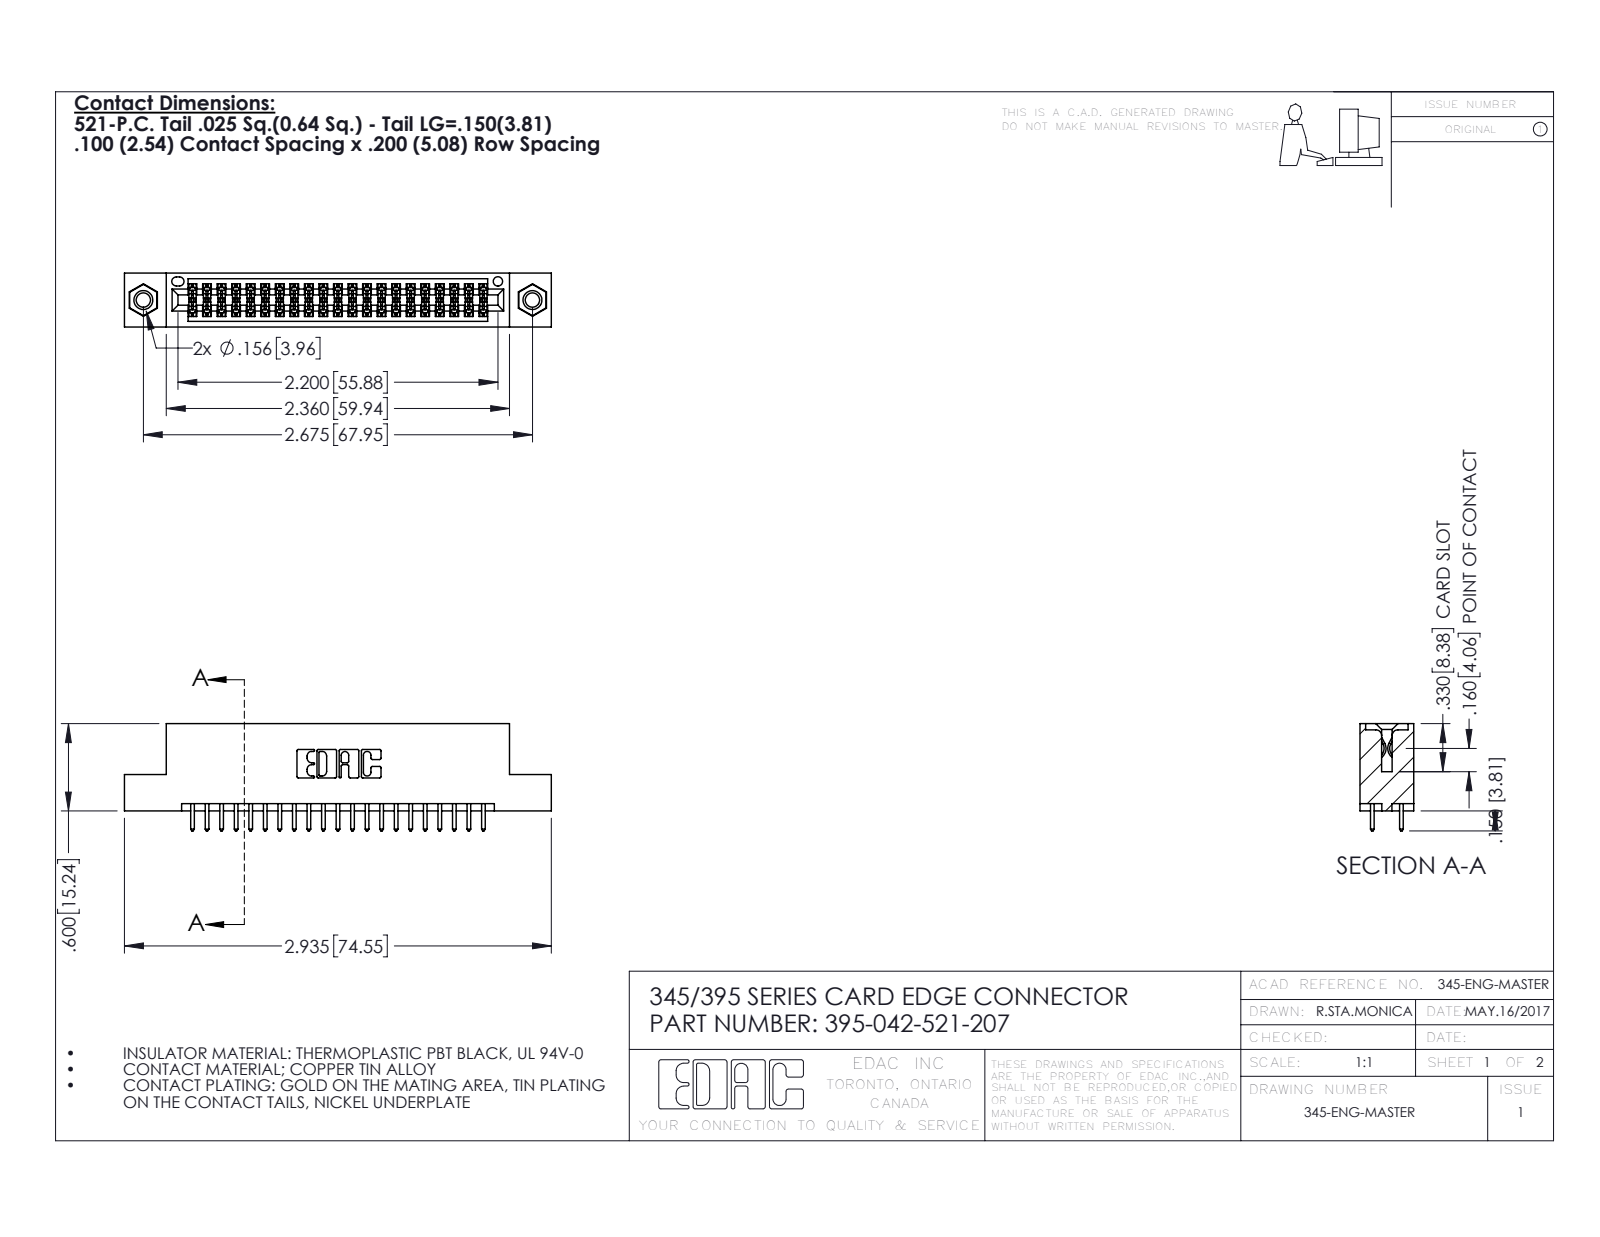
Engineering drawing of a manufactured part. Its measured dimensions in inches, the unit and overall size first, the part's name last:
Units: inches
Overall size (bounding box): 2.935 × 0.737 × 0.37
Round holes (diameter × count): ⌀0.098 ×2, ⌀0.125 ×2, ⌀0.156 ×2, ⌀0.064 ×1
Round bosses / shafts (diameter × count): ⌀0.155 ×2
Partial cylindrical surfaces — rounded edges, fillets, slot ends (radius × count): R0.006 ×63, R0.01 ×42, R0.01 ×22, R0.007 ×6, R0.031 ×6, R0.026 ×3, R0.014 ×2, R0.019 ×2
Main face-to-face distances: 0.072, 0.298, 0.2, 0.37, 0.098, 0.272, 0.025, 0.225, 0.175, 0.149
Hole centre spacings: 0.27, 2.441, 2.675
Volume: 0.428 in³ · Surface area: 15.32 in²
Bodies: 45 solids, 2286 faces (1498 planar, 772 cylindrical, 16 other)
Part name (STEP PRODUCT): 345-292-001_345-293-121; 345-250-001_345-250-005-103; 395-042-521-207; 345 Part_Flush Mounting Lugs - 0.156 Dia-TI
STEP written by: SolidWorks 2016 (CONFIG_CONTROL_DESIGN)
